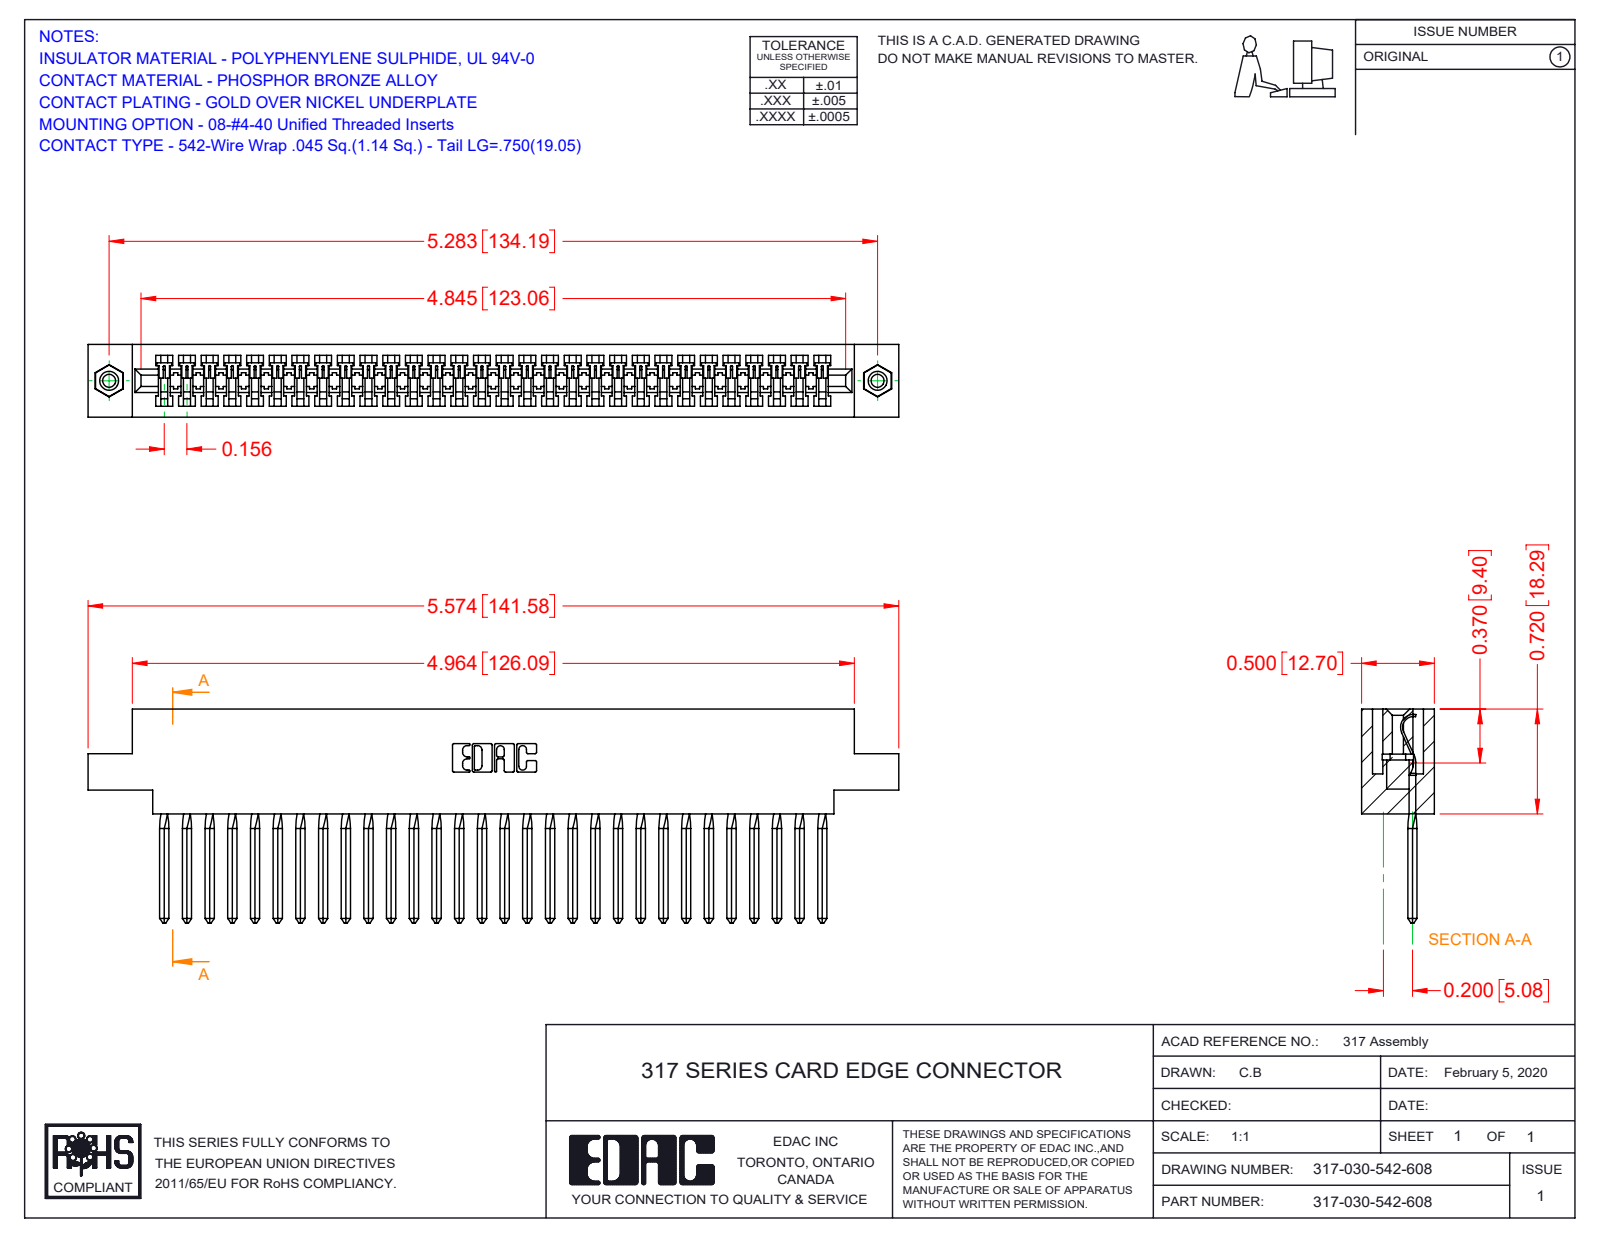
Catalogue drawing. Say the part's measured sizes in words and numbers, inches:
The part is named "317-030-542-608; 317-290-003_542; 345-250-001_345-250-003-102; 317 Part_.156 Dia - TI". Its 3-D file was written by "SolidWorks 2016 (CONFIG_CONTROL_DESIGN)". It is 33 solids with 2412 faces: 2010 planar, 266 cylindrical and 136 other. Overall it measures 5.574 by 1.47 by 0.5 inches. Its volume is 1.315 cubic inches and its surface area 40.36 square inches. Round holes: 2 of diameter 0.089, 2 of diameter 0.125, 2 of diameter 0.156. Round bosses or shafts: 2 of diameter 0.155. Partial cylindrical surfaces (rounded edges, fillets, slot ends): 60 of radius 0.006, 22 of radius 0.01, 6 of radius 0.007, 6 of radius 0.031, 3 of radius 0.026, 1 of radius 0.074, 1 of radius 0.089, 1 of radius 0.1. The main face-to-face distances are 0.5, 0.075, 0.425, 0.35, 0.11, 0.136, 0.72, 0.211, 0.289, 0.213. The hole center spacings are 5.283.
